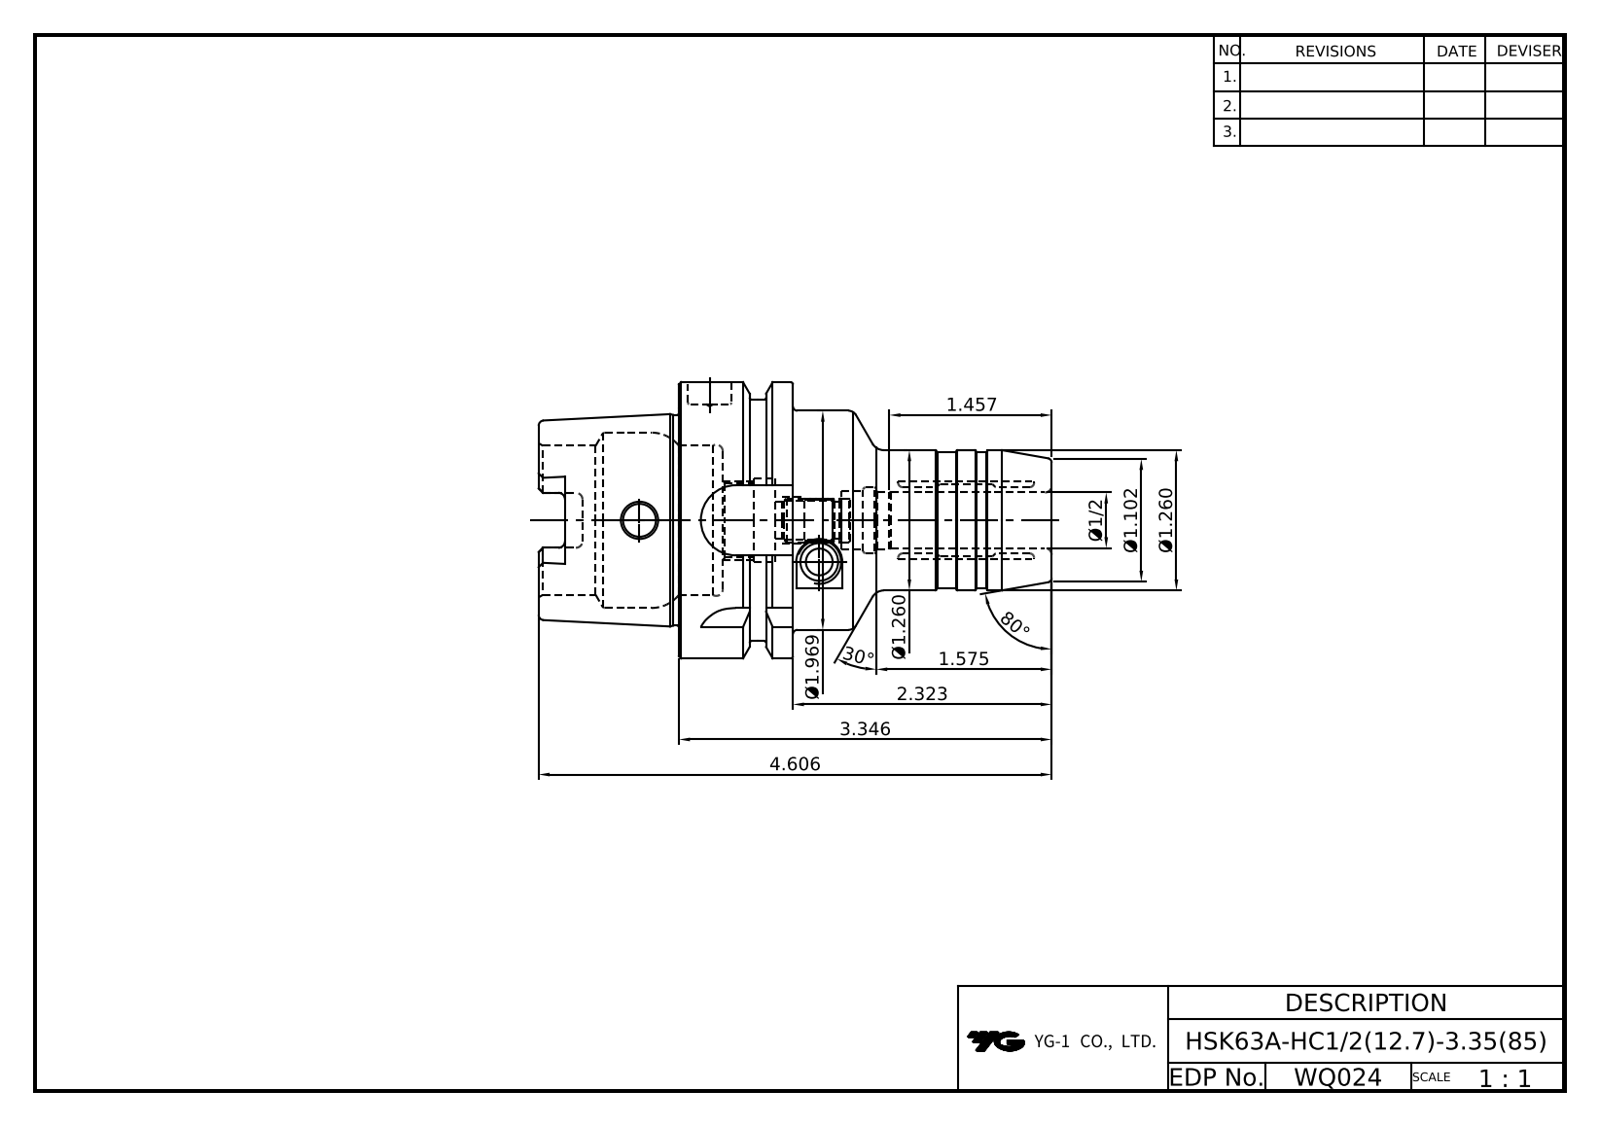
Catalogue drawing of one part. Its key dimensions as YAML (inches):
part_name: "LO-HSK63A-HC9_525-80"
step_written_by: "CREO PARAMETRIC BY PTC INC, 2018500 (CONFIG_CONTROL_DESIGN)"
units: inches
bodies: {solids: 1, faces: 209, planar: 58, cylindrical: 63, other: 88}
overall_size: [4.606, 2.48, 2.48]
volume: 8.475
surface_area: 48.28
round_holes:
  - {diameter: 0.394, count: 2}
  - {diameter: 0.295, count: 1}
  - {diameter: 0.331, count: 1}
  - {diameter: 0.417, count: 1}
  - {diameter: 0.5, count: 1}
  - {diameter: 0.52, count: 1}
  - {diameter: 0.669, count: 1}
  - {diameter: 0.709, count: 1}
  - {diameter: 0.748, count: 1}
  - {diameter: 1.339, count: 1}
  - {diameter: 1.575, count: 1}
round_bosses_or_shafts:
  - {diameter: 2.48, count: 1}
  - {diameter: 2.165, count: 1}
  - {diameter: 1.969, count: 1}
  - {diameter: 1.891, count: 1}
  - {diameter: 1.26, count: 1}
  - {diameter: 1.22, count: 1}
partial_cylinders:
  - {radius: 0.059, count: 6}
  - {radius: 0.113, count: 4}
  - {radius: 0.315, count: 4}
face_to_face_distances: [1.024, 0.394, 0.63, 1.26, 2.323, 3.346, 2.953, 0.241, 0.389, 1.654]
